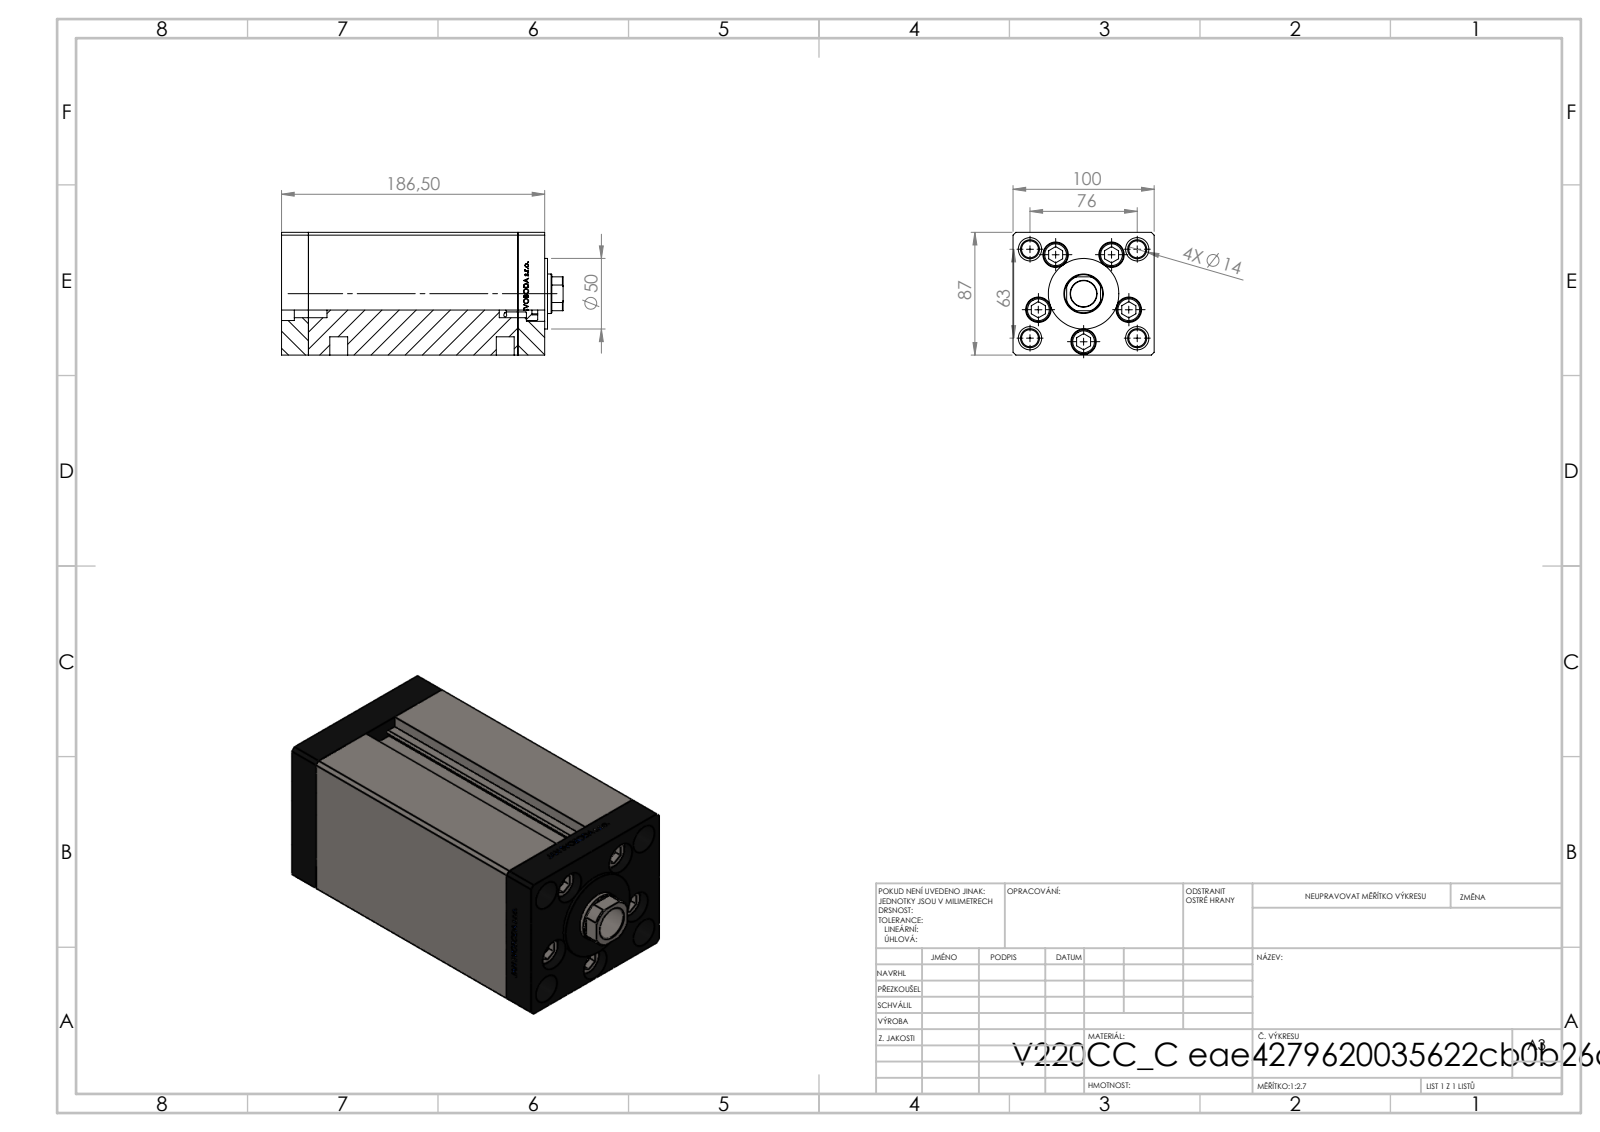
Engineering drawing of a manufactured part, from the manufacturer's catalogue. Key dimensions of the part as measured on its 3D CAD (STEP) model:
Part name (STEP PRODUCT): V220C BACK_C; V220C_VC_C; ALLEN BOLT; V220C FRONT (+1 more)
STEP written by: SolidWorks 2019 (CONFIG_CONTROL_DESIGN)
Units: millimetres
Bodies: 13 solids, 1182 faces (544 planar, 176 cylindrical, 462 other)
Overall size (bounding box): 199.5 × 100 × 87
Volume: 1 328 000 mm³ · Surface area: 230 838 mm²
Round holes (diameter × count): ⌀13.5 ×9, ⌀18 ×5, ⌀2 ×4, ⌀12 ×4, ⌀13.16 ×4, ⌀16.5 ×4, ⌀17 ×1, ⌀18.5 ×1, ⌀28 ×1
Round bosses / shafts (diameter × count): ⌀8 ×5, ⌀17 ×4, ⌀50 ×1
Partial cylindrical surfaces — rounded edges, fillets, slot ends (radius × count): R0.93 ×2, R13.5 ×1
Main face-to-face distances: 100, 87, 19, 148.5, 167.5, 34.25, 186.5, 152.25, 133.25, 15.25
Hole centre spacings: 34, 49.36, 18.59, 21.03, 38.08, 39.27, 40.83, 43.24
